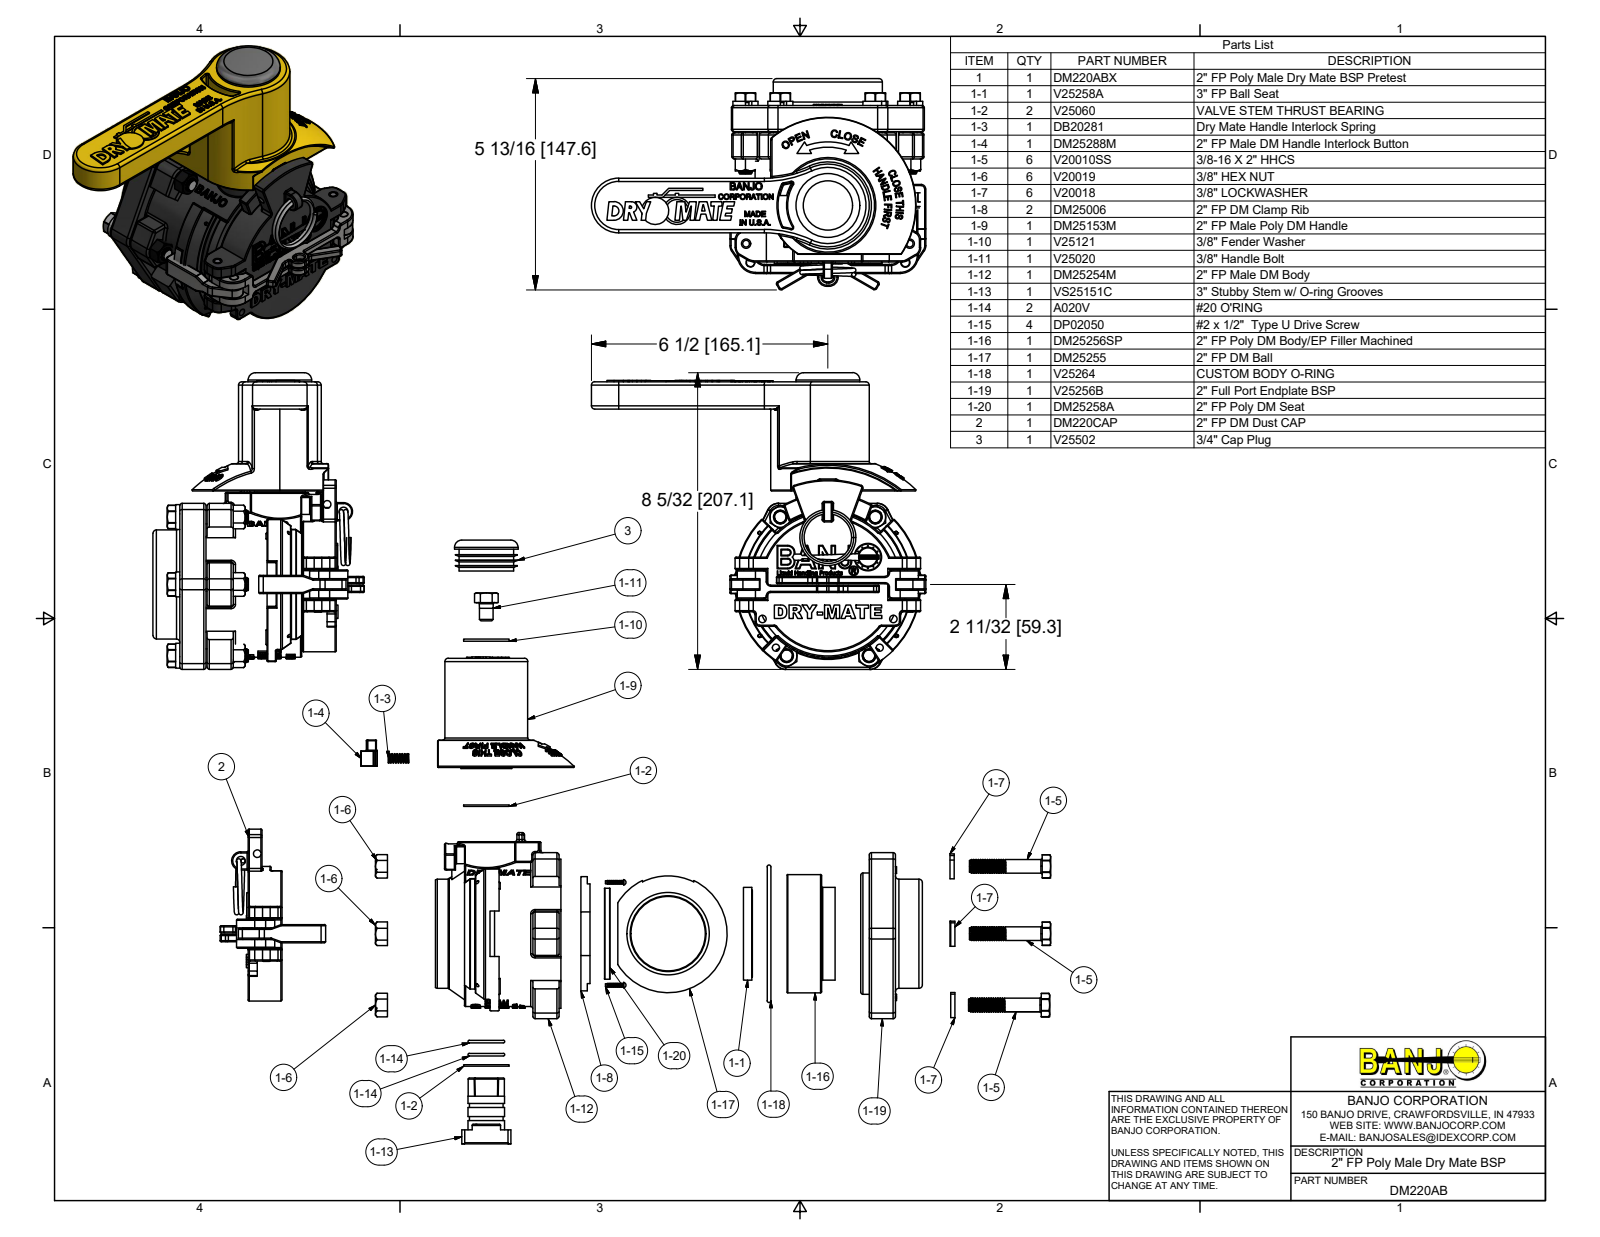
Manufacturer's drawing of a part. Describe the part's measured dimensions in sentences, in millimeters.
The part is named "DM220AB; DM220ABX; DM25254M; DM25254MY (+8 more)". Its 3-D file was written by "Autodesk Inventor 2017 (AUTOMOTIVE_DESIGN)". It is 53 solids with 5911 faces: 2102 planar, 1465 cylindrical and 2344 other. Overall it measures 233.5 by 207.14 by 147.57 millimeters. Its volume is 1 071 000 cubic millimeters and its surface area 374 634 square millimeters. Round holes: 7 of diameter 10.31, 6 of diameter 7.81, 6 of diameter 9.78, 6 of diameter 11.43, 5 of diameter 6.35, 4 of diameter 2.18, 4 of diameter 3.3, 4 of diameter 5.08, 2 of diameter 6.6, 2 of diameter 52.07, 1 of diameter 5.33, 1 of diameter 7.8. Round bosses or shafts: 90 of diameter 8.24, 7 of diameter 9.52, 6 of diameter 17.46, 4 of diameter 2.08, 2 of diameter 6.6, 2 of diameter 6.53, 2 of diameter 6.32, 1 of diameter 101.6. Partial cylindrical surfaces (rounded edges, fillets, slot ends): 286 of radius 0.76, 66 of radius 1.52, 30 of radius 0.51, 27 of radius 6.35, 24 of radius 0.25, 13 of radius 7.94, 12 of radius 1.59, 12 of radius 2.29. The main face-to-face distances are 3.81, 105.41, 109.22, 5.08, 16.51, 17.78, 38.1, 87.63, 91.44, 67.31. The hole center spacings are 37.25, 59.69, 111.16, 9.32, 11.95, 13.56, 14.09, 18.27.
